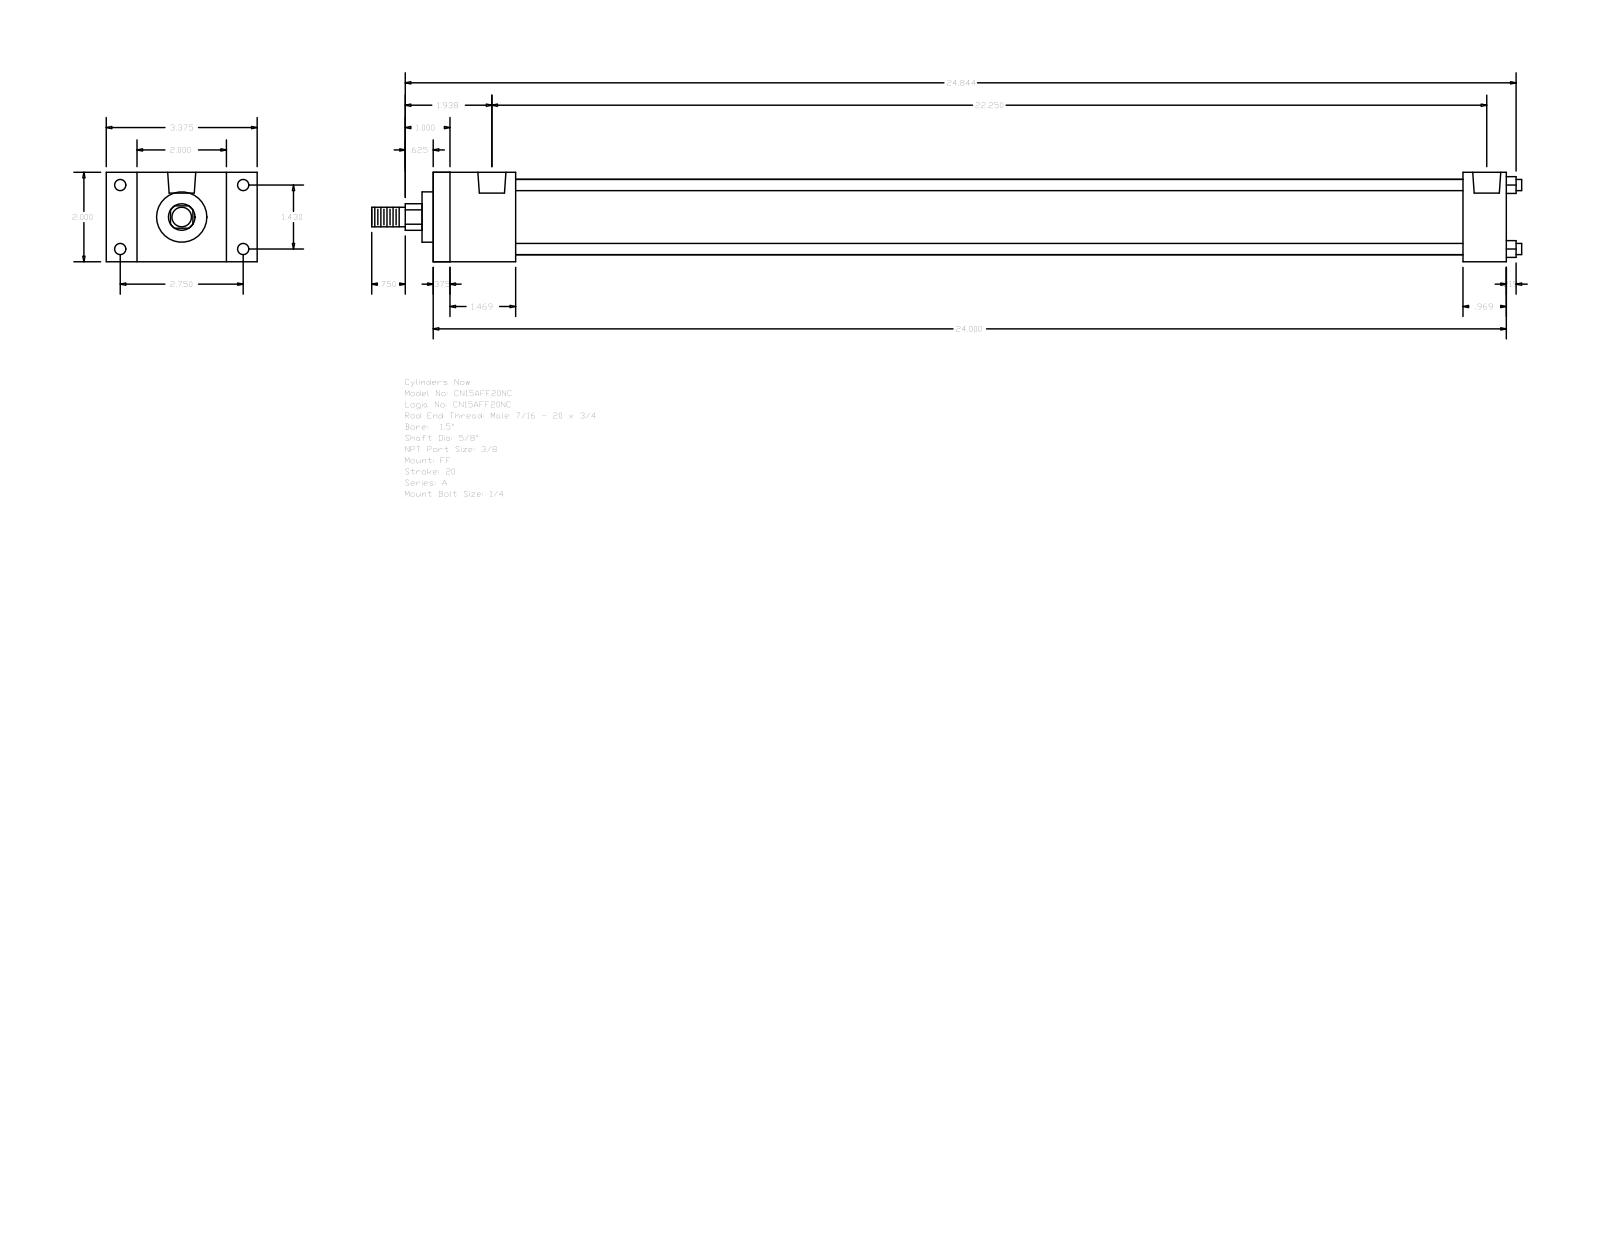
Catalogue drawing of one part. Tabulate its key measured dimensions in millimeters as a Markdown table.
| quantity | value |
| --- | --- |
| part name | A_FF__0150_0.625 |
| STEP written by | GSSL Pune (CONFIG_CONTROL_DESIGN) |
| units | millimeters |
| bodies | 0 solids, 92 faces (64 planar, 28 cylindrical, 0 other) |
| overall size | 653.26 × 85.72 × 50.8 |
| round holes (diameter × count) | 5.56 × 4, 6.35 × 4, 15.93 × 2 |
| round bosses / shafts (diameter × count) | 6.35 × 4, 42.93 × 1, 28.57 × 1, 15.88 × 1, 11.11 × 1 |
| partial cylindrical surfaces (radius × count) | 7.54 × 1 |
| main face-to-face distances | 50.8, 609.6, 9.52, 600.08, 46.83, 584.99, 37.31, 575.47, 538.16, 562.77 |
| hole center spacings | 3.97, 36.32, 69.84, 78.72, 557.21, 561.18, 565.15 |
